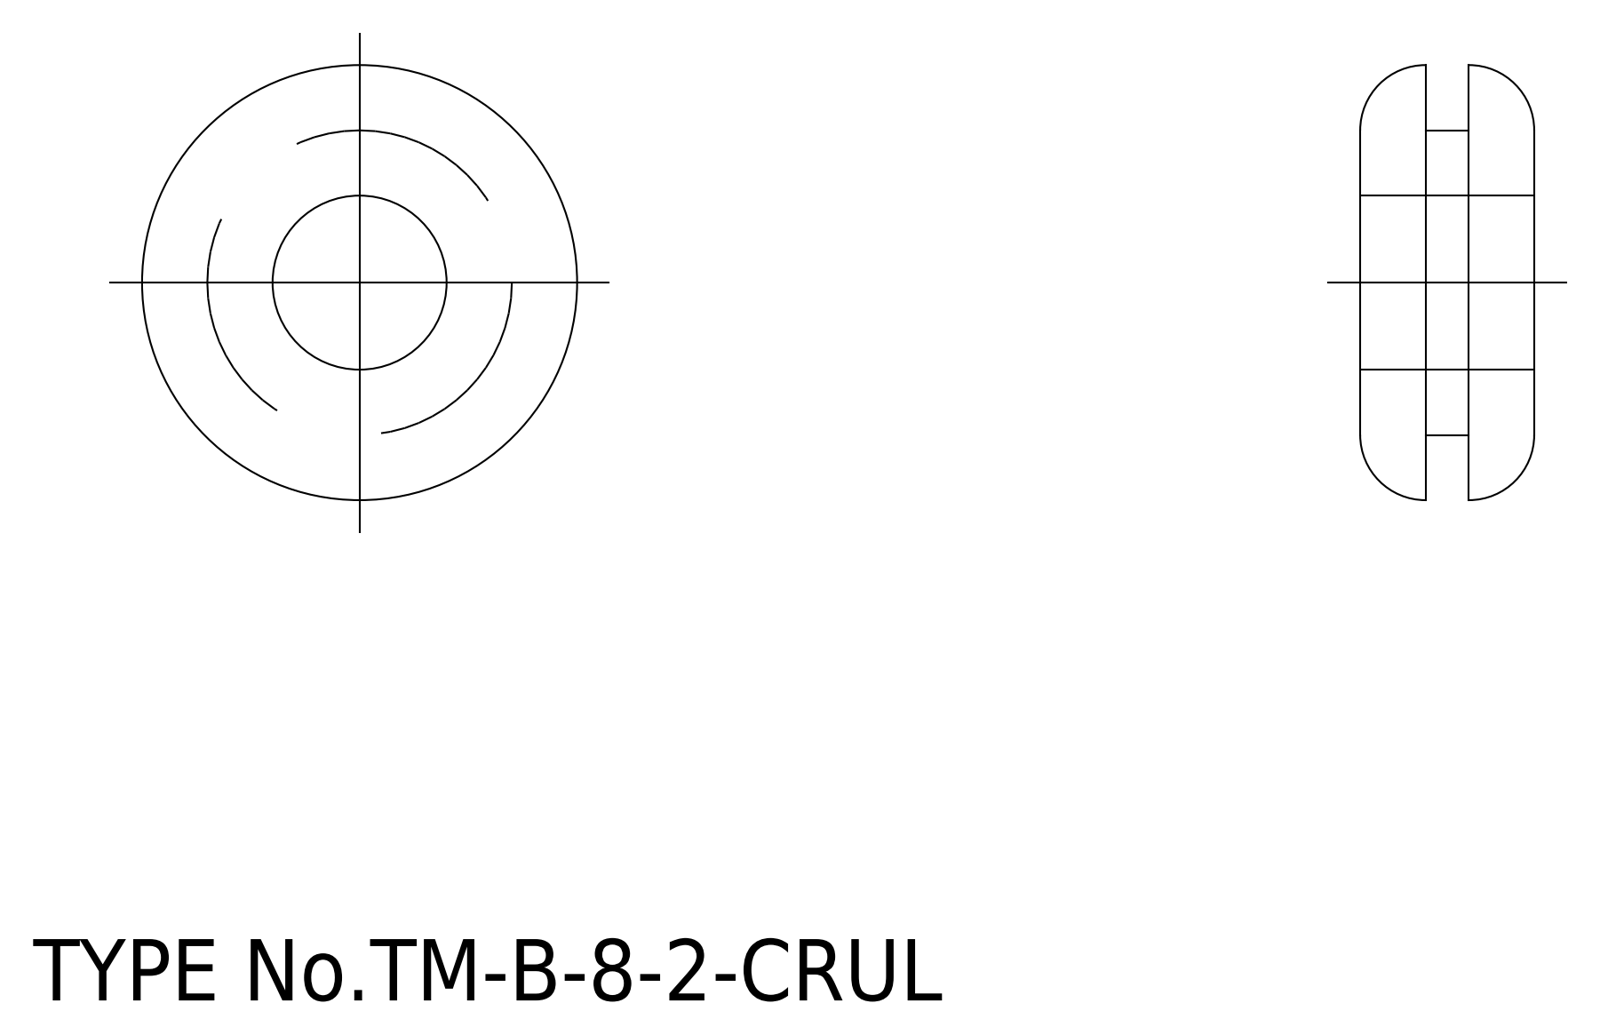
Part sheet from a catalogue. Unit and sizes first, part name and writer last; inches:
Units: inches
Overall size (bounding box): 0.787 × 0.787 × 0.315
Round holes (diameter × count): ⌀0.315 ×1
Round bosses / shafts (diameter × count): ⌀0.551 ×1
Main face-to-face distances: 0.118, 0.197, 0.079, 0.315
Volume: 0.096 in³ · Surface area: 2.085 in²
Bodies: 1 solid, 12 faces (4 planar, 4 cylindrical, 4 other)
STEP written by: spGate 15.6.1 (AUTOMOTIVE_DESIGN)
